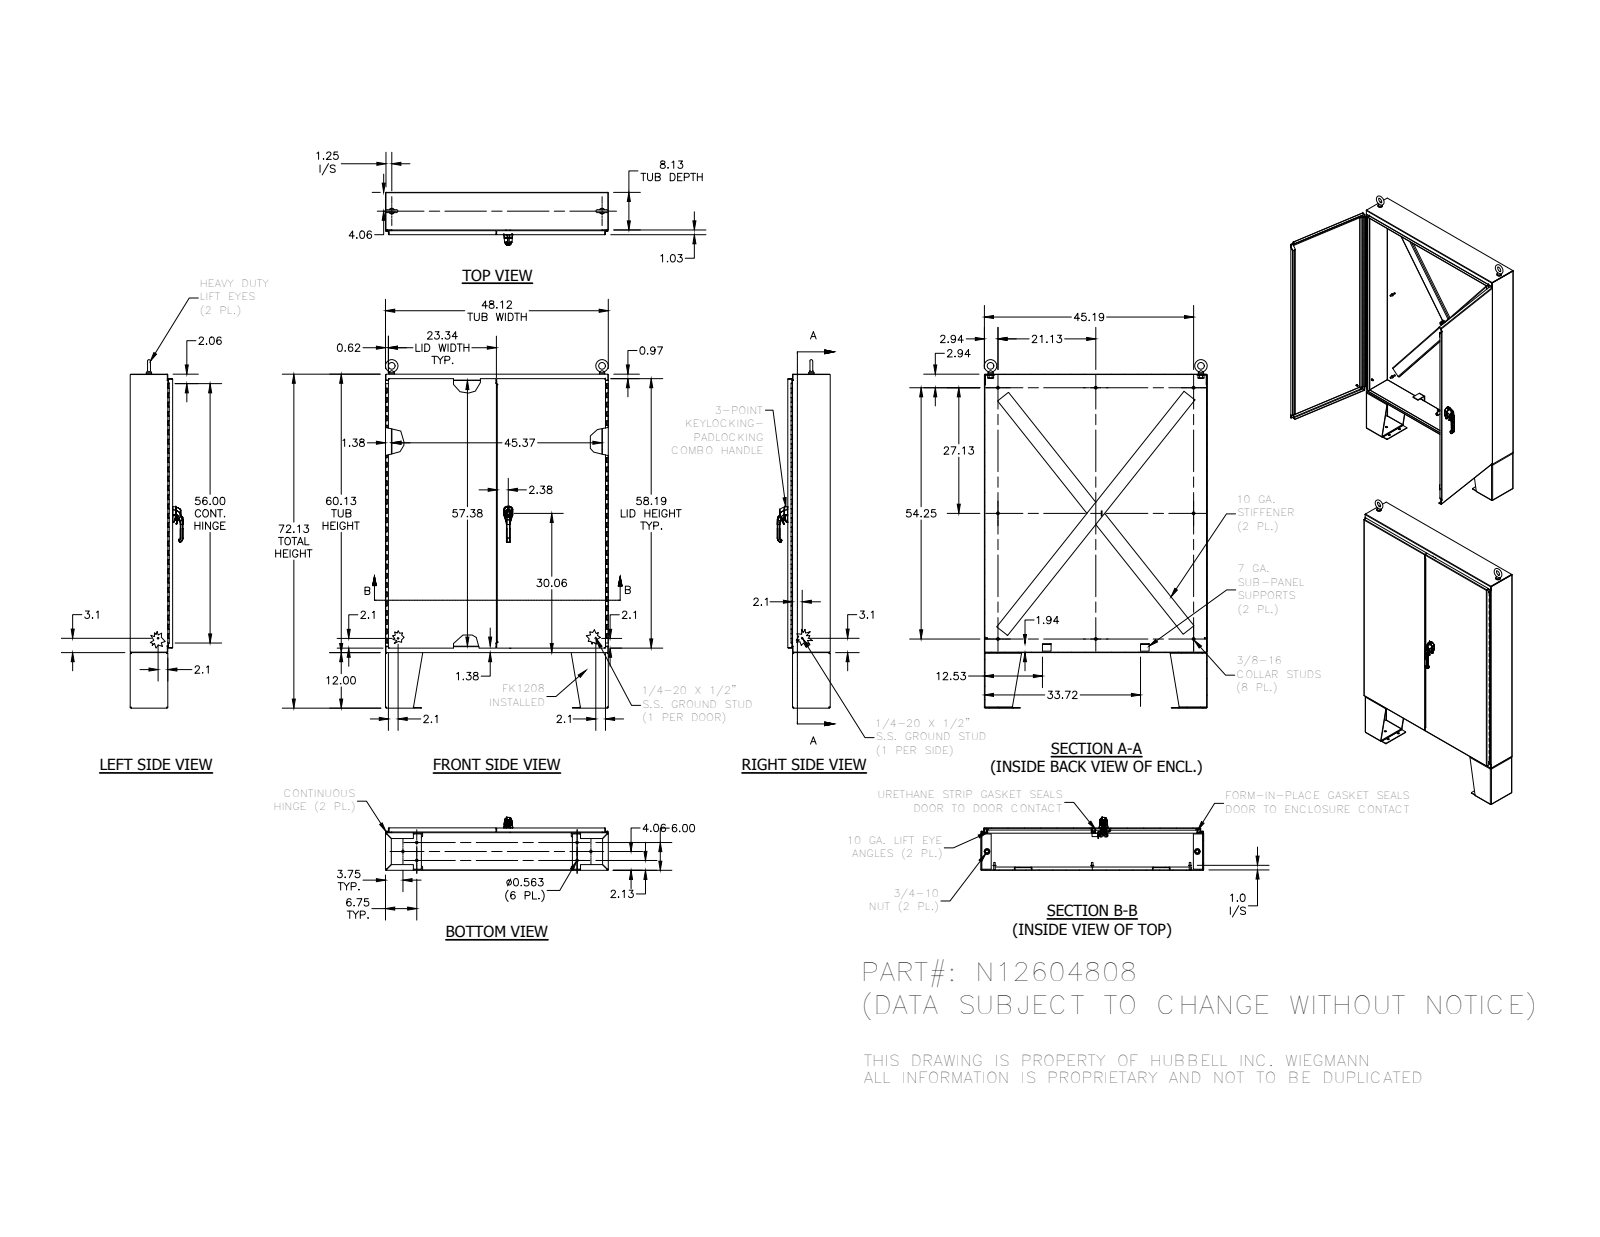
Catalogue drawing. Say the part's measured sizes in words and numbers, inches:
The part is named "N12604808". Its 3-D file was written by "SolidWorks 2018 (AUTOMOTIVE_DESIGN)". It is 74 solids with 2388 faces: 1376 planar, 712 cylindrical and 300 other. Overall it measures 75.248 by 48.125 by 15.33 inches. Its volume is 1 133 cubic inches and its surface area 22 550 square inches. Round holes: 18 of diameter 0.563, 8 of diameter 0.277, 4 of diameter 0.2, 3 of diameter 0.28, 2 of diameter 0.125, 2 of diameter 0.241, 2 of diameter 0.25, 2 of diameter 0.252, 2 of diameter 0.4, 2 of diameter 0.45, 2 of diameter 0.642, 2 of diameter 0.813. Round bosses or shafts: 8 of diameter 0.33, 5 of diameter 0.625, 5 of diameter 0.25, 3 of diameter 0.625, 3 of diameter 0.337, 2 of diameter 1.25, 2 of diameter 1.12, 2 of diameter 1. Partial cylindrical surfaces (rounded edges, fillets, slot ends): 28 of radius 0.031, 23 of radius 0.094, 22 of radius 0.219, 19 of radius 0.125, 18 of radius 0.05, 16 of radius 0.025, 13 of radius 0.03, 8 of radius 0.067. The main face-to-face distances are 0.094, 13.058, 13.067, 12.965, 12.973, 13.152, 0.085, 13.16, 0.102, 60.031. The hole center spacings are 2.041, 4.89, 5, 6.064, 6.503, 9.84, 10.75, 11.147.
